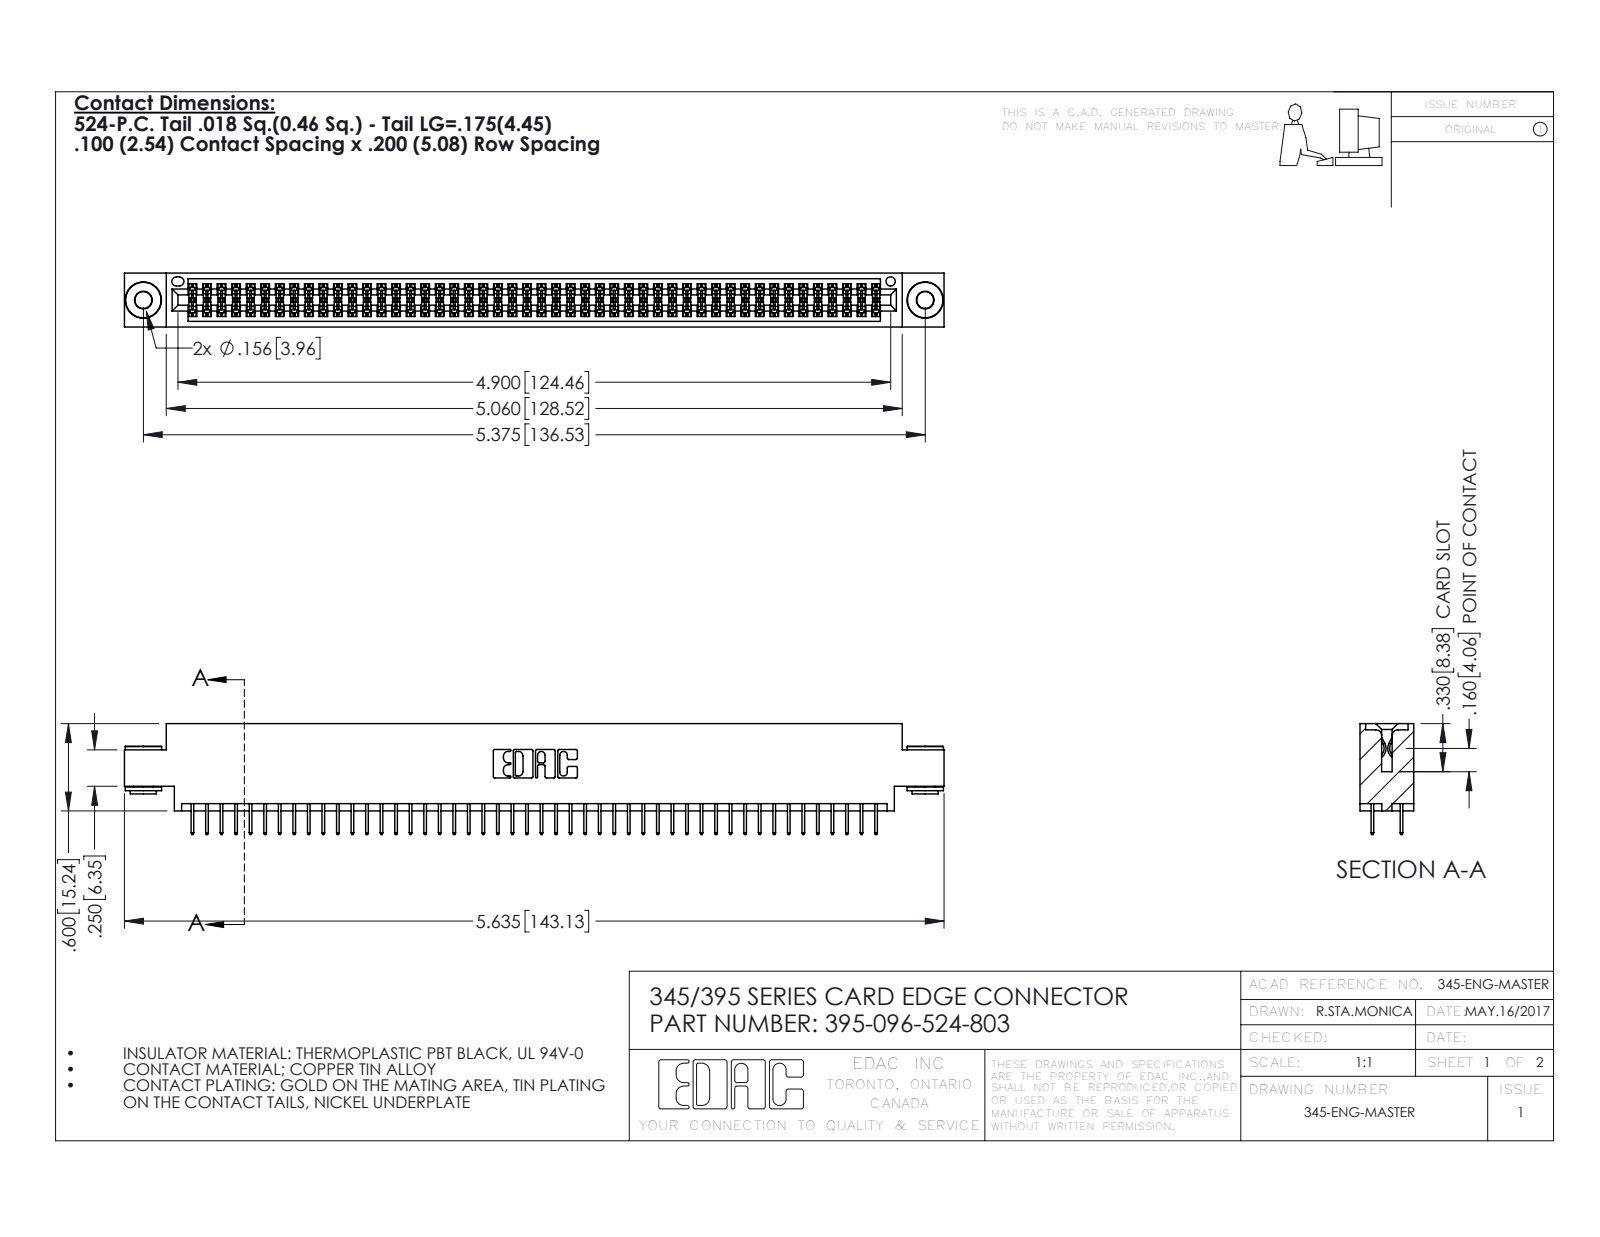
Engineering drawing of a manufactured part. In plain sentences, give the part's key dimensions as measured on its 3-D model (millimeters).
The part is named "345 Part_0.170 Offset - 0.156 Dia-TH; 395-096-524-803; 345-250-002_345-250-002-102; 345-292-001_345-293-124". Its 3-D file was written by "SolidWorks 2016 (CONFIG_CONTROL_DESIGN)". It is 99 solids with 5352 faces: 3838 planar, 1506 cylindrical and 8 other. Overall it measures 143.1 by 19.4 by 9.4 millimeters. Its volume is 13 700 cubic millimeters and its surface area 20 360 square millimeters. Round holes: 2 of diameter 2.9, 2 of diameter 4, 1 of diameter 1.6. Round bosses or shafts: 2 of diameter 6.4, 2 of diameter 4.6, 2 of diameter 3.5. Partial cylindrical surfaces (rounded edges, fillets, slot ends): 144 of radius 0.2, 22 of radius 0.3, 6 of radius 0.2, 6 of radius 0.8, 3 of radius 0.7, 2 of radius 0.4, 2 of radius 0.5, 2 of radius 0.6. The main face-to-face distances are 1.8, 7.6, 9.4, 5.1, 2.5, 6.9, 0.6, 5.7, 4.4, 1.8. The hole center spacings are 6.9, 130.5, 136.5.
